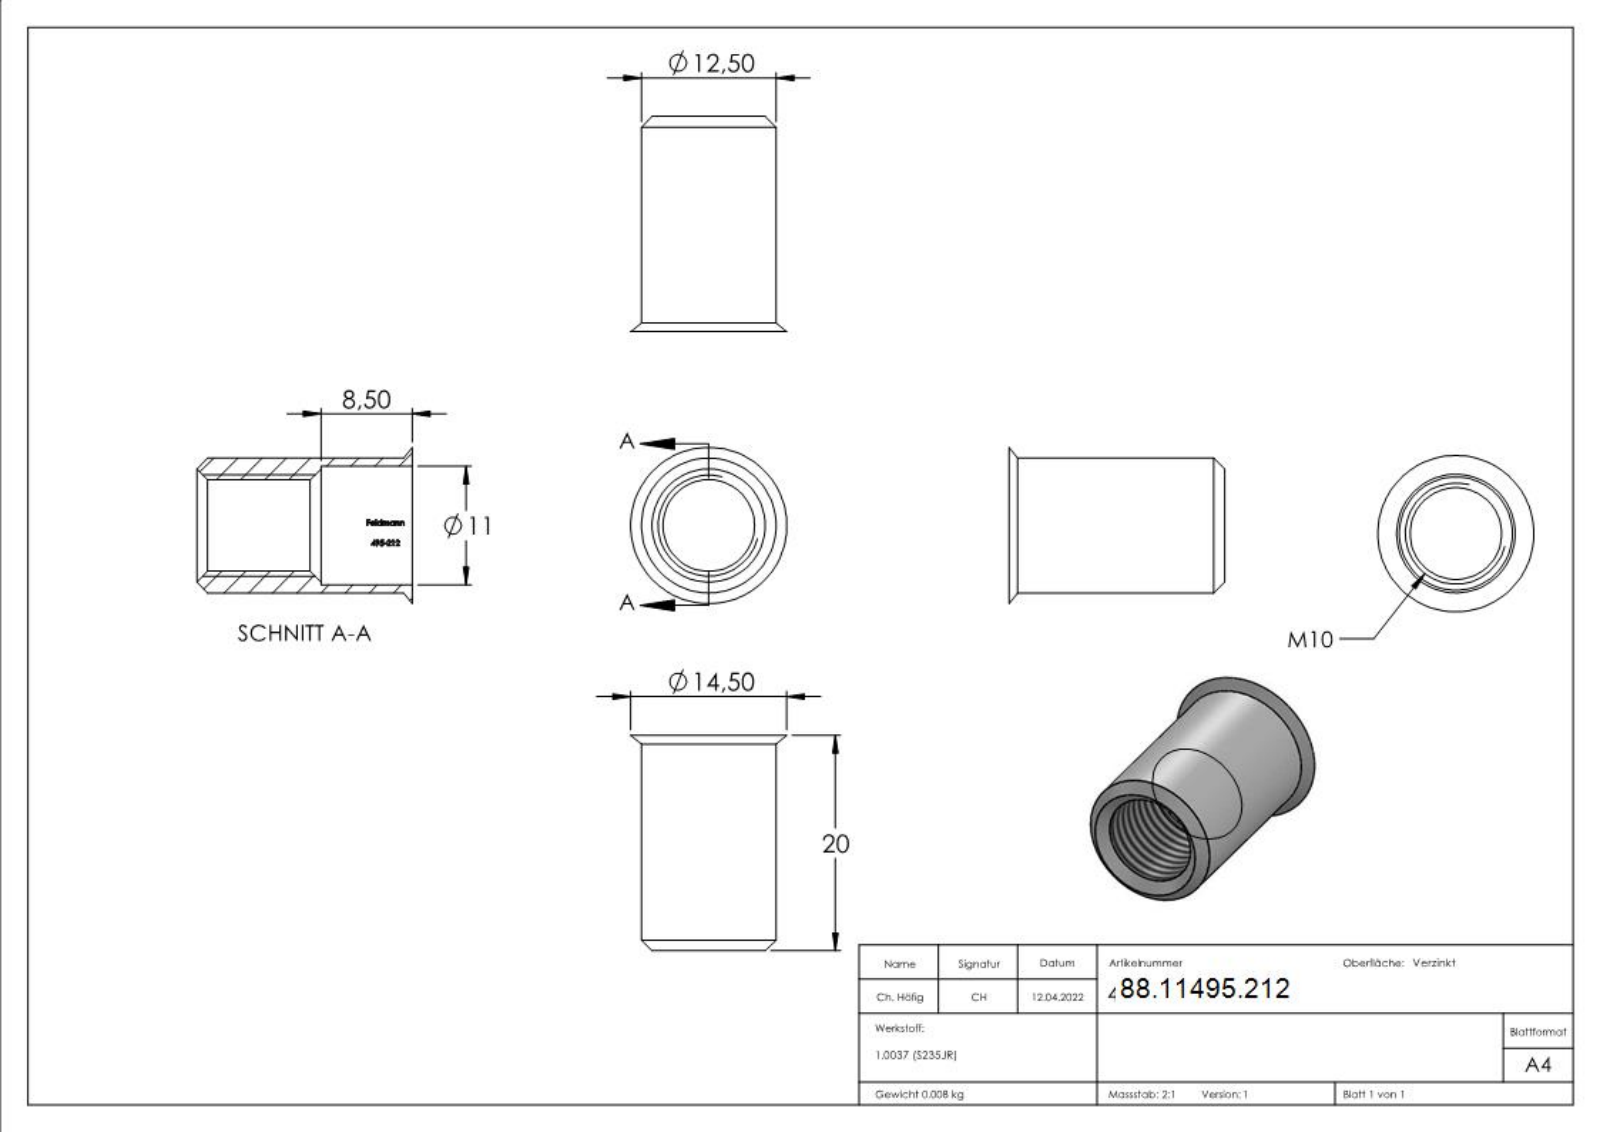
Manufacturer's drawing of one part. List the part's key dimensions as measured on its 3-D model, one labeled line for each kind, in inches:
Part name (STEP PRODUCT): 495-212
STEP written by: SolidWorks 2018 (CONFIG_CONTROL_DESIGN)
Units: inches
Bodies: 1 solid, 210 faces (100 planar, 29 cylindrical, 81 other)
Overall size (bounding box): 0.787 × 0.571 × 0.571
Volume: 0.059 in³ · Surface area: 2.378 in²
Round holes (diameter × count): ⌀0.335 ×1, ⌀0.433 ×1
Round bosses / shafts (diameter × count): ⌀0.492 ×1
Partial cylindrical surfaces — rounded edges, fillets, slot ends (radius × count): R0.22 ×1
Main face-to-face distances: 0.335, 0.072, 0.026, 0.053, 0.074, 0.047, 0.066, 0.069, 0.064, 0.07
